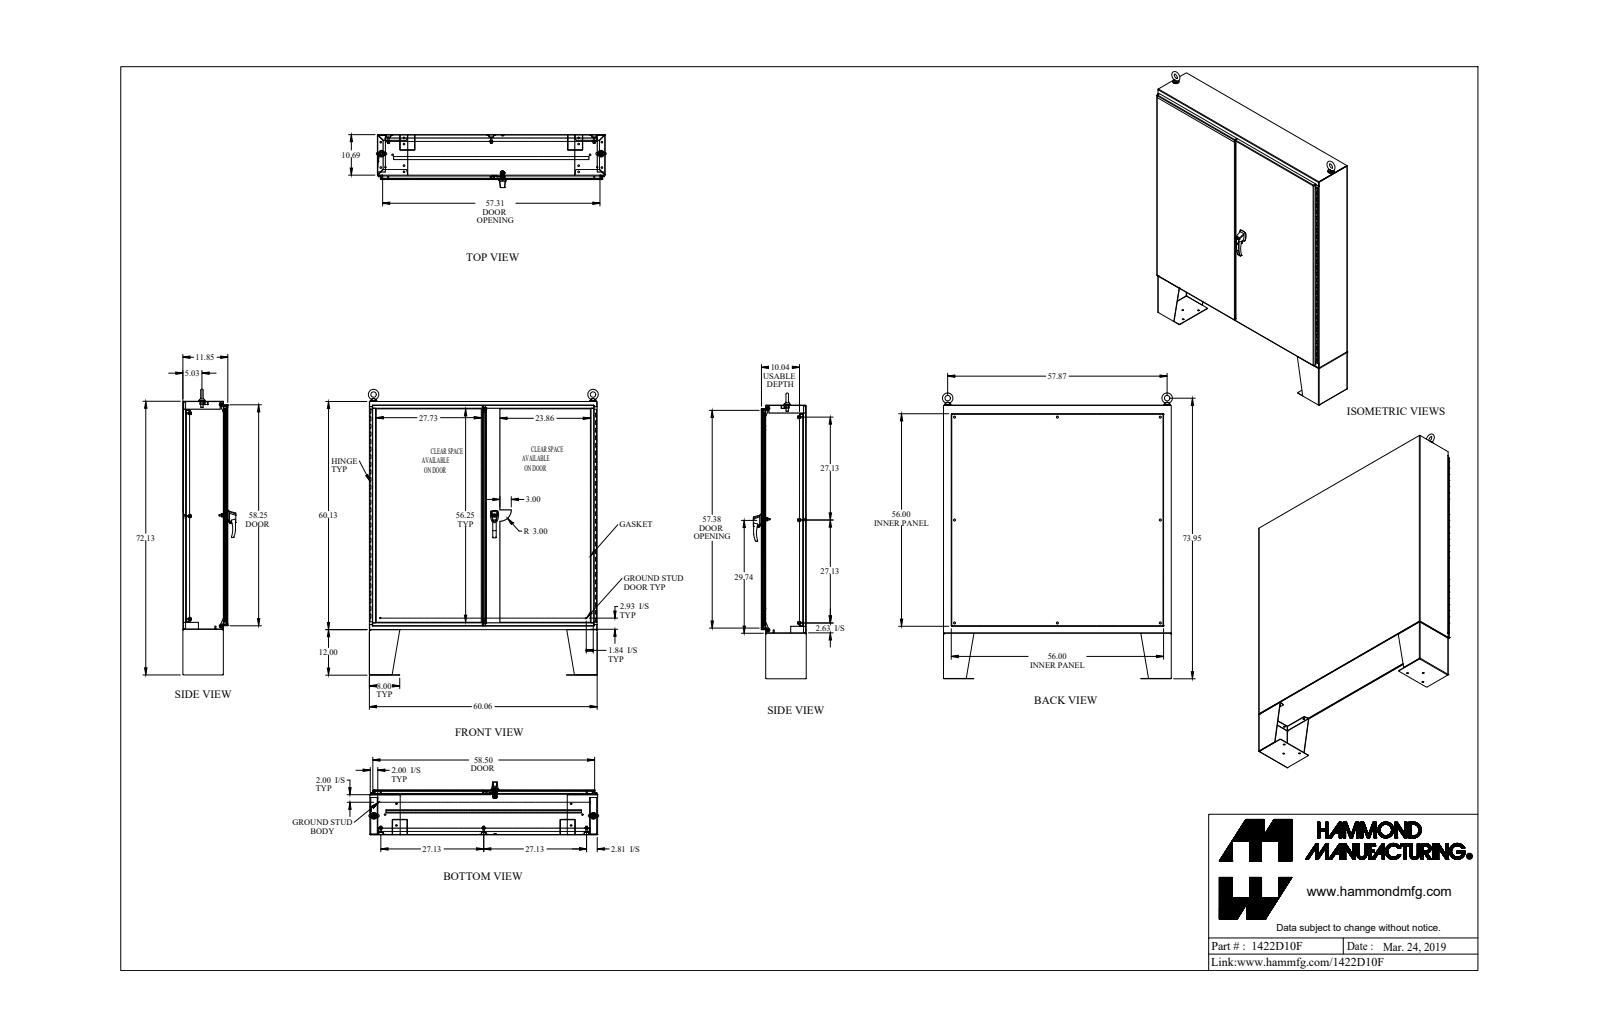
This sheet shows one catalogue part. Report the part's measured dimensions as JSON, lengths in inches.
{"part_name": "1422D10F_Default", "step_written_by": "SolidWorks 2019 (CONFIG_CONTROL_DESIGN)", "units": "inches", "bodies": {"solids": 90, "faces": 2769, "planar": 1280, "cylindrical": 1242, "other": 247}, "overall_size": [75.778, 61.121, 13.963], "volume_in3": 1634, "surface_area_in2": 32320, "round_holes": [[0.304, 20], [0.437, 14], [0.307, 9], [0.563, 8], [0.445, 6], [0.11, 2], [0.25, 2], [0.257, 2], [0.28, 2], [0.281, 2], [0.313, 2], [0.39, 2]], "round_bosses_or_shafts": [[1, 10], [0.65, 8], [0.375, 8], [0.33, 8], [0.281, 6], [0.25, 4], [1.75, 2], [1.5, 2]], "partial_cylinders_radius": [[0.048, 32], [0.143, 32], [0.125, 22], [0.018, 16], [0.06, 14], [0.116, 12], [0.05, 8], [0.185, 8]], "face_to_face_distances": [0.095, 0.095, 11.658, 11.753, 11.753, 11.848, 0.125, 10.066, 9.971, 1.687], "hole_center_spacings": [6, 58.7, 12, 59.613, 18, 61.104, 24, 63.132]}
